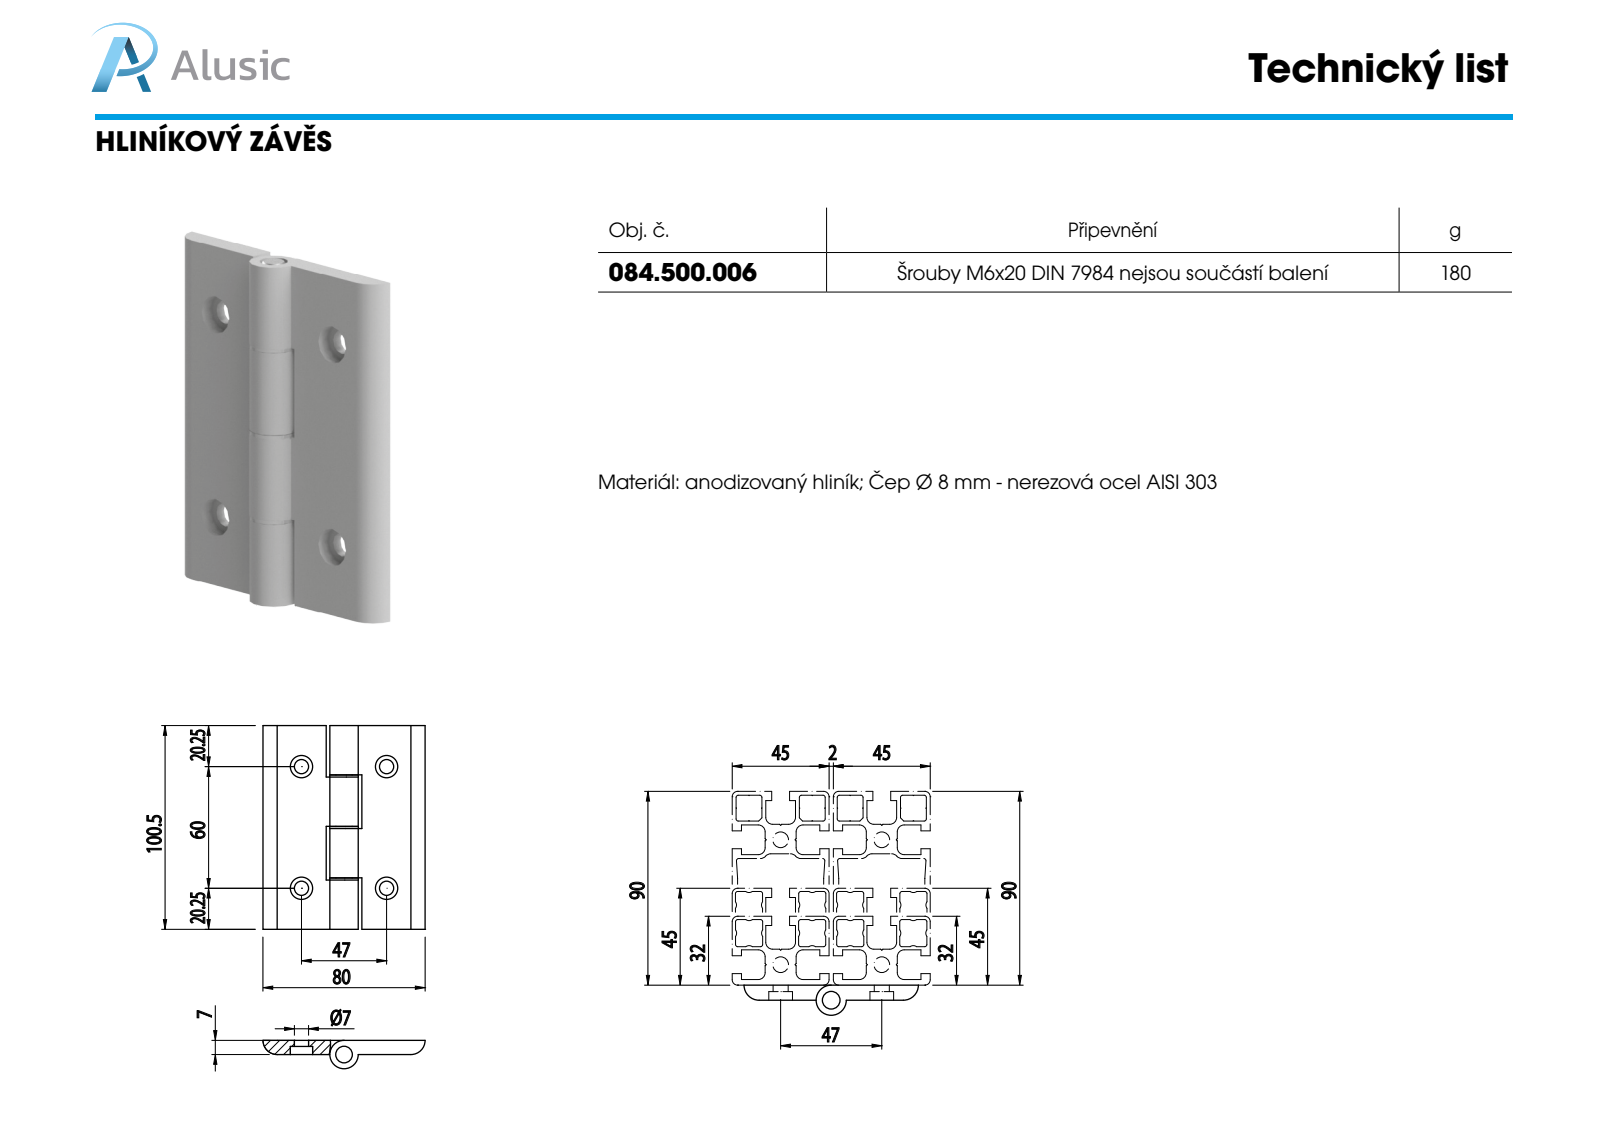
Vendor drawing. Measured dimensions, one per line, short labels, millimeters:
name: 084.500.006; SEMI CERNIERA_084.500.005.A; 084.500.001.C
written by: SolidWorks 2011 (CONFIG_CONTROL_DESIGN)
unit: mm
bodies: 5 solids, 70 faces (28 planar, 42 cylindrical, 0 other)
size: 100 × 81 × 14.1
volume: 50 985 mm³; area: 23 984 mm²
holes: 4× ⌀6.6, 4× ⌀11, 1× ⌀8.1, 1× ⌀8.2
bosses: 1× ⌀14.1, 1× ⌀14
rounds: 2× R6.7
face distances: 6.7, 1, 100, 25, 25.5, 24.25, 75.75, 25.25, 74.75, 50.5
hole spacings: 47, 60, 76.22
